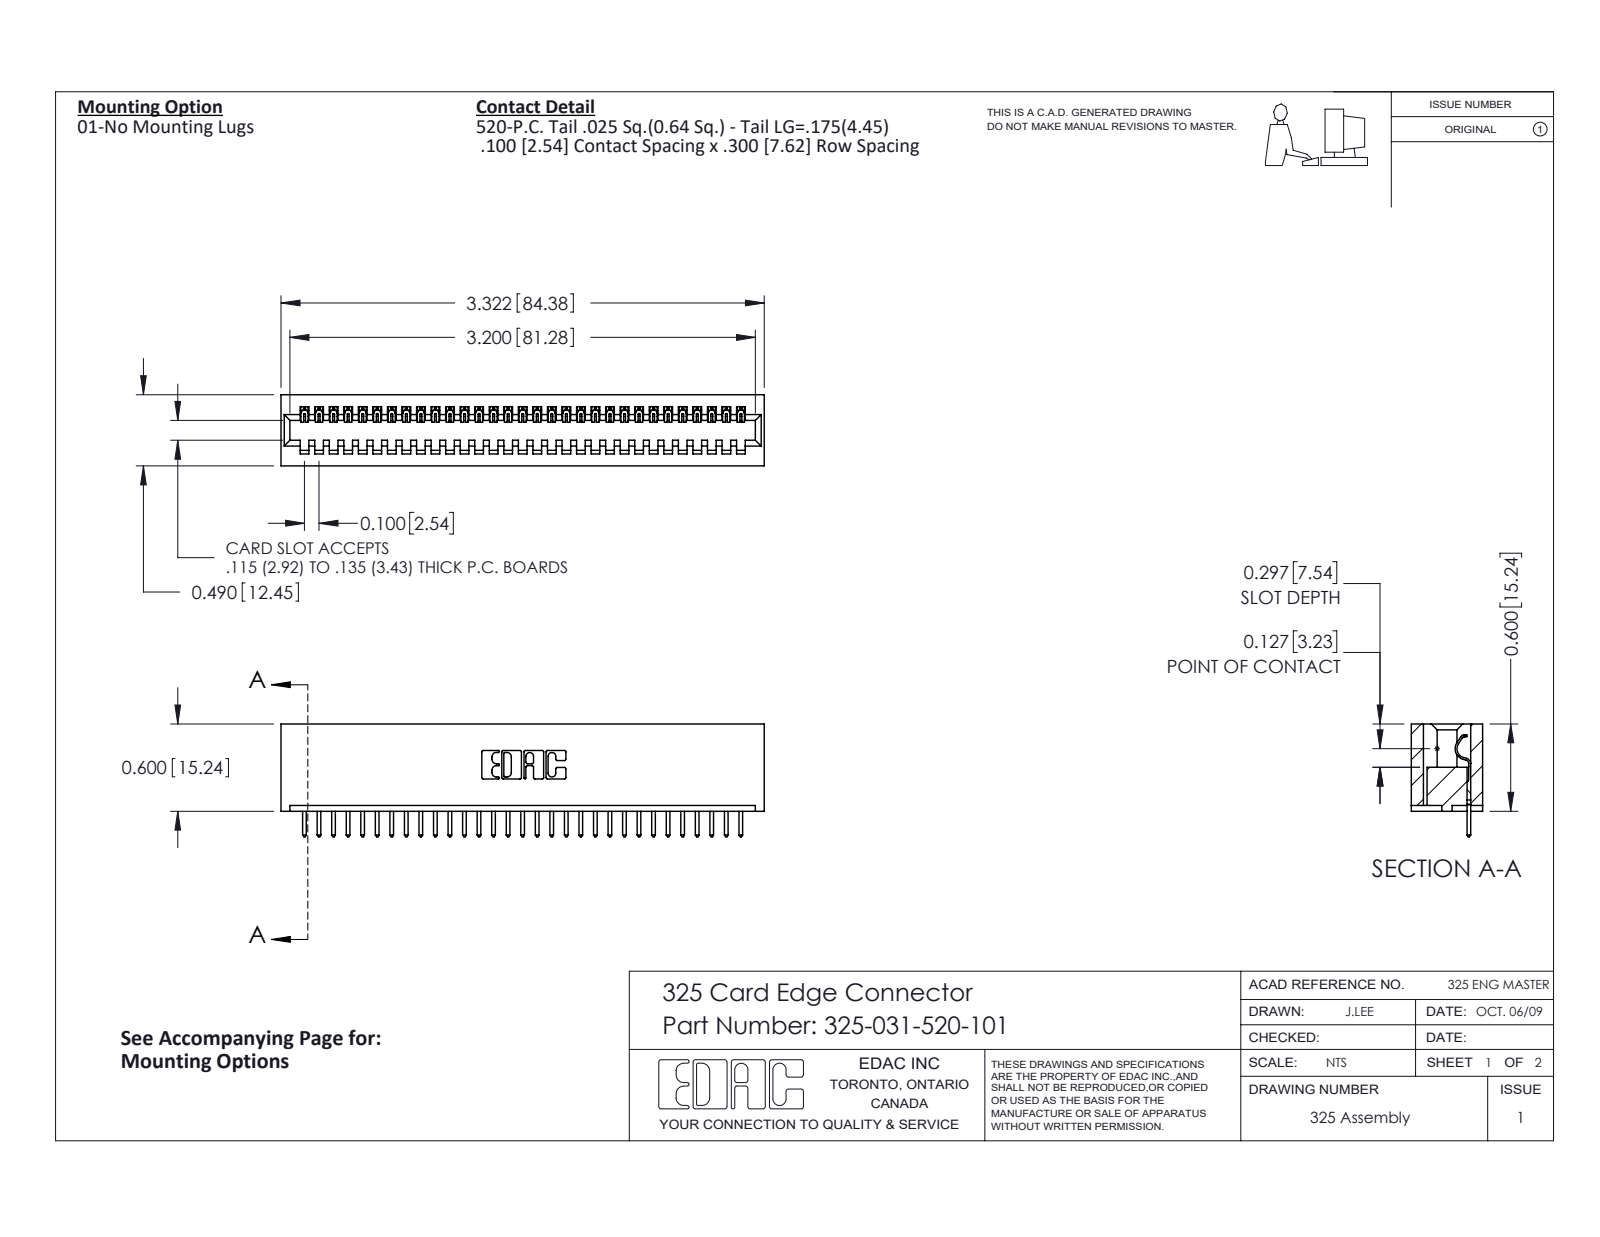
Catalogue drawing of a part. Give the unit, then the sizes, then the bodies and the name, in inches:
Units: inches
Overall size (bounding box): 3.322 × 0.775 × 0.49
Partial cylindrical surfaces — rounded edges, fillets, slot ends (radius × count): R0.006 ×62, R0.01 ×62, R0.01 ×22, R0.007 ×6, R0.031 ×6, R0.026 ×3, R0.014 ×1, R0.022 ×1
Main face-to-face distances: 0.083, 0.407, 0.3, 0.49, 0.107, 0.383, 0.025, 0.325, 0.1, 0.2
Volume: 0.678 in³ · Surface area: 18.79 in²
Bodies: 32 solids, 1904 faces (1368 planar, 536 cylindrical, 0 other)
Part name (STEP PRODUCT): 325 Part_Lugless; 325-292-001_325-293-120; 325-031-520-101
STEP written by: SolidWorks 2016 (CONFIG_CONTROL_DESIGN)
